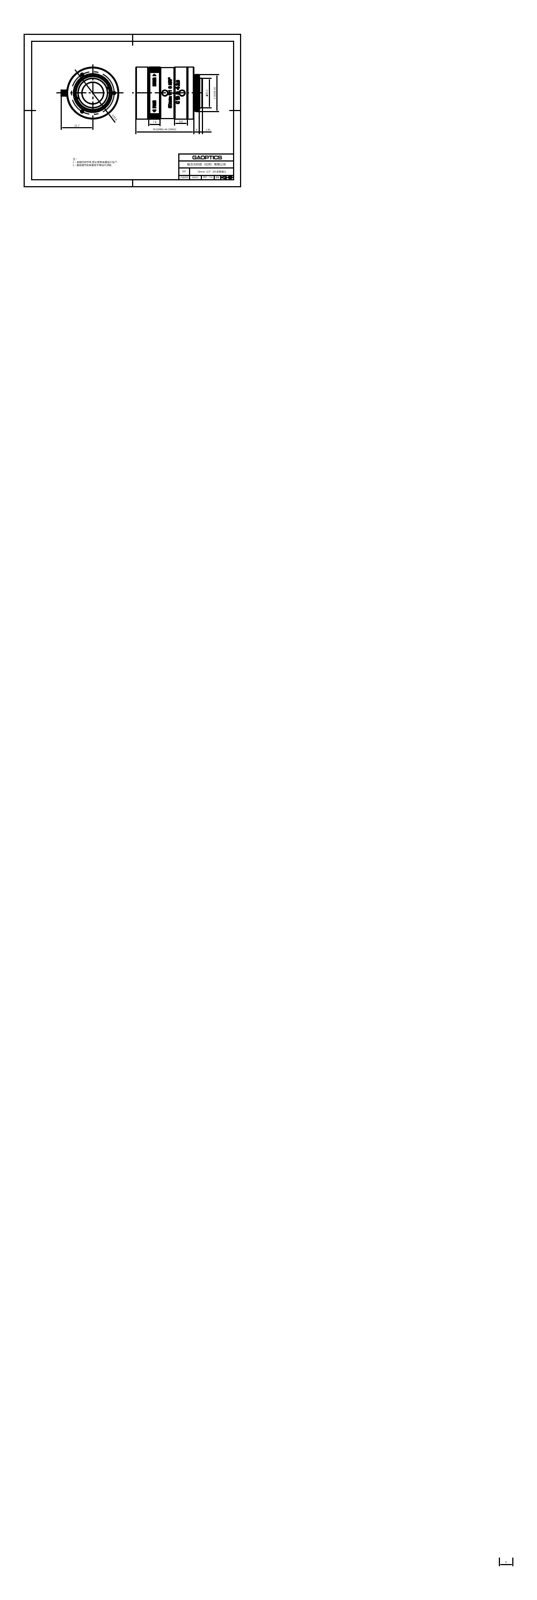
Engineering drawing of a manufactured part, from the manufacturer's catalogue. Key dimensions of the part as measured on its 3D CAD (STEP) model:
Part name (STEP PRODUCT): 600004
STEP written by: SolidWorks 2020 (CONFIG_CONTROL_DESIGN)
Units: millimetres
Bodies: 14 solids, 1400 faces (475 planar, 359 cylindrical, 566 other)
Overall size (bounding box): 45.54 × 40.09 × 35.6
Volume: 39 136 mm³ · Surface area: 17 960 mm²
Round holes (diameter × count): ⌀1.4 ×5, ⌀2 ×4, ⌀0.9 ×3, ⌀1.3 ×3, ⌀1.2 ×2, ⌀13 ×1, ⌀13.6 ×1, ⌀15 ×1, ⌀16 ×1, ⌀18 ×1, ⌀22.5 ×1, ⌀25 ×1
Round bosses / shafts (diameter × count): ⌀2 ×2, ⌀35.6 ×1, ⌀35 ×1, ⌀34.8 ×1, ⌀34.49 ×1, ⌀33.3 ×1, ⌀32.4 ×1, ⌀30.5 ×1
Partial cylindrical surfaces — rounded edges, fillets, slot ends (radius × count): R0.5 ×6, R2 ×2, R16.3 ×1, R16.85 ×1, R17.3 ×1, R17.58 ×1, R17.61 ×1, R17.9 ×1
Main face-to-face distances: 1, 0.86, 0.9, 1.04, 1.9, 6.14, 7.04, 29.16, 30.06, 30.2
Hole centre spacings: 14, 24.25, 24.24
